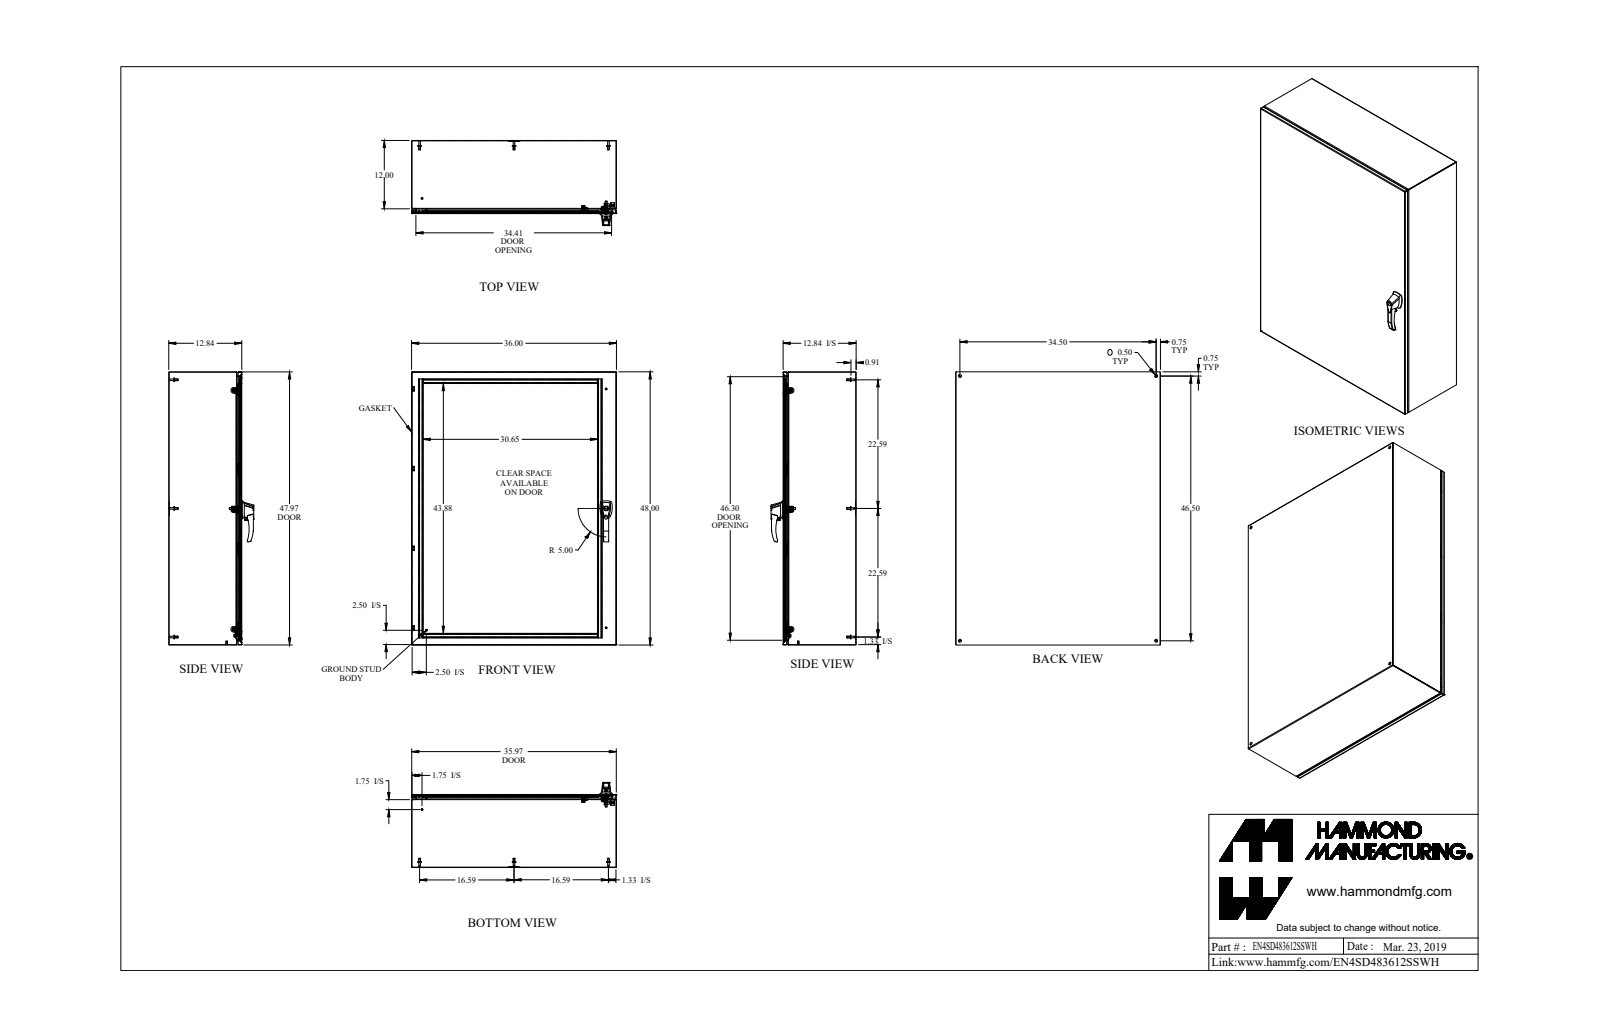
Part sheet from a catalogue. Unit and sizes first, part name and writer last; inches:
Units: inches
Overall size (bounding box): 48 × 36 × 14.958
Round holes (diameter × count): ⌀0.176 ×6, ⌀0.5 ×4, ⌀0.196 ×3, ⌀0.25 ×3, ⌀0.265 ×3, ⌀0.313 ×3, ⌀0.413 ×3, ⌀0.256 ×2, ⌀0.375 ×2, ⌀0.394 ×2, ⌀0.172 ×1, ⌀0.233 ×1
Round bosses / shafts (diameter × count): ⌀0.313 ×10, ⌀0.275 ×8, ⌀0.25 ×7, ⌀0.625 ×6, ⌀0.375 ×6, ⌀0.156 ×6, ⌀1 ×3, ⌀0.625 ×3
Partial cylindrical surfaces — rounded edges, fillets, slot ends (radius × count): R0.048 ×32, R0.01 ×24, R0.036 ×18, R0.108 ×18, R0.062 ×17, R0.094 ×10, R0.016 ×9, R0.125 ×9
Main face-to-face distances: 0.072, 12.771, 12.699, 12.843, 35.928, 35.856, 36, 0.072, 47.856, 47.928
Hole centre spacings: 0.786, 41.969, 20.436, 20.984, 20.985, 21, 21.547, 23.274
Volume: 463.4 in³ · Surface area: 12 760 in²
Bodies: 68 solids, 1787 faces (779 planar, 667 cylindrical, 341 other)
Part name (STEP PRODUCT): EN4SD483612SSWH
STEP written by: SolidWorks 2018 (AUTOMOTIVE_DESIGN)
